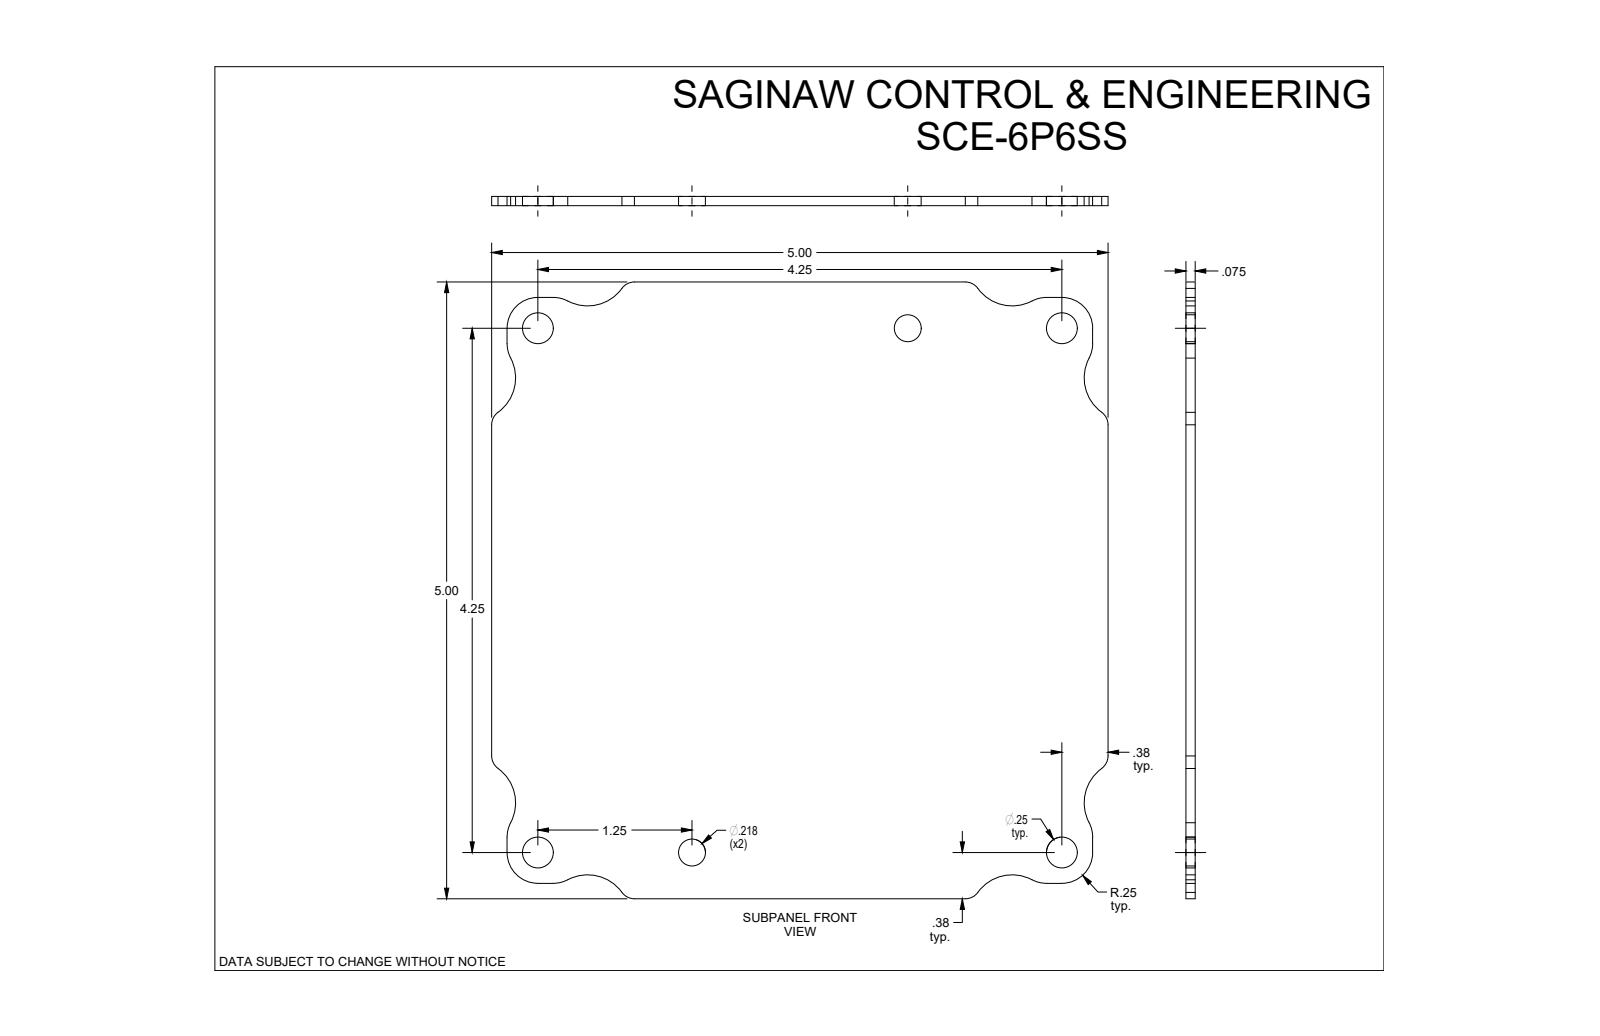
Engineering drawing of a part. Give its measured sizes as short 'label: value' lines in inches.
name: SCE-6P6SS
written by: SolidWorks 2019 (CONFIG_CONTROL_DESIGN)
unit: in
bodies: 1 solid, 48 faces (14 planar, 34 cylindrical, 0 other)
size: 5 × 5 × 0.075
volume: 1.765 in³; area: 48.83 in²
holes: 4× ⌀0.25, 2× ⌀0.218
rounds: 12× R0.25, 8× R0.125, 8× R0.344
face distances: 0.075, 5, 0.125, 4.875, 4.75
hole spacings: 4.25, 1.25, 3, 4.43, 5.202, 6.01, 4.596
